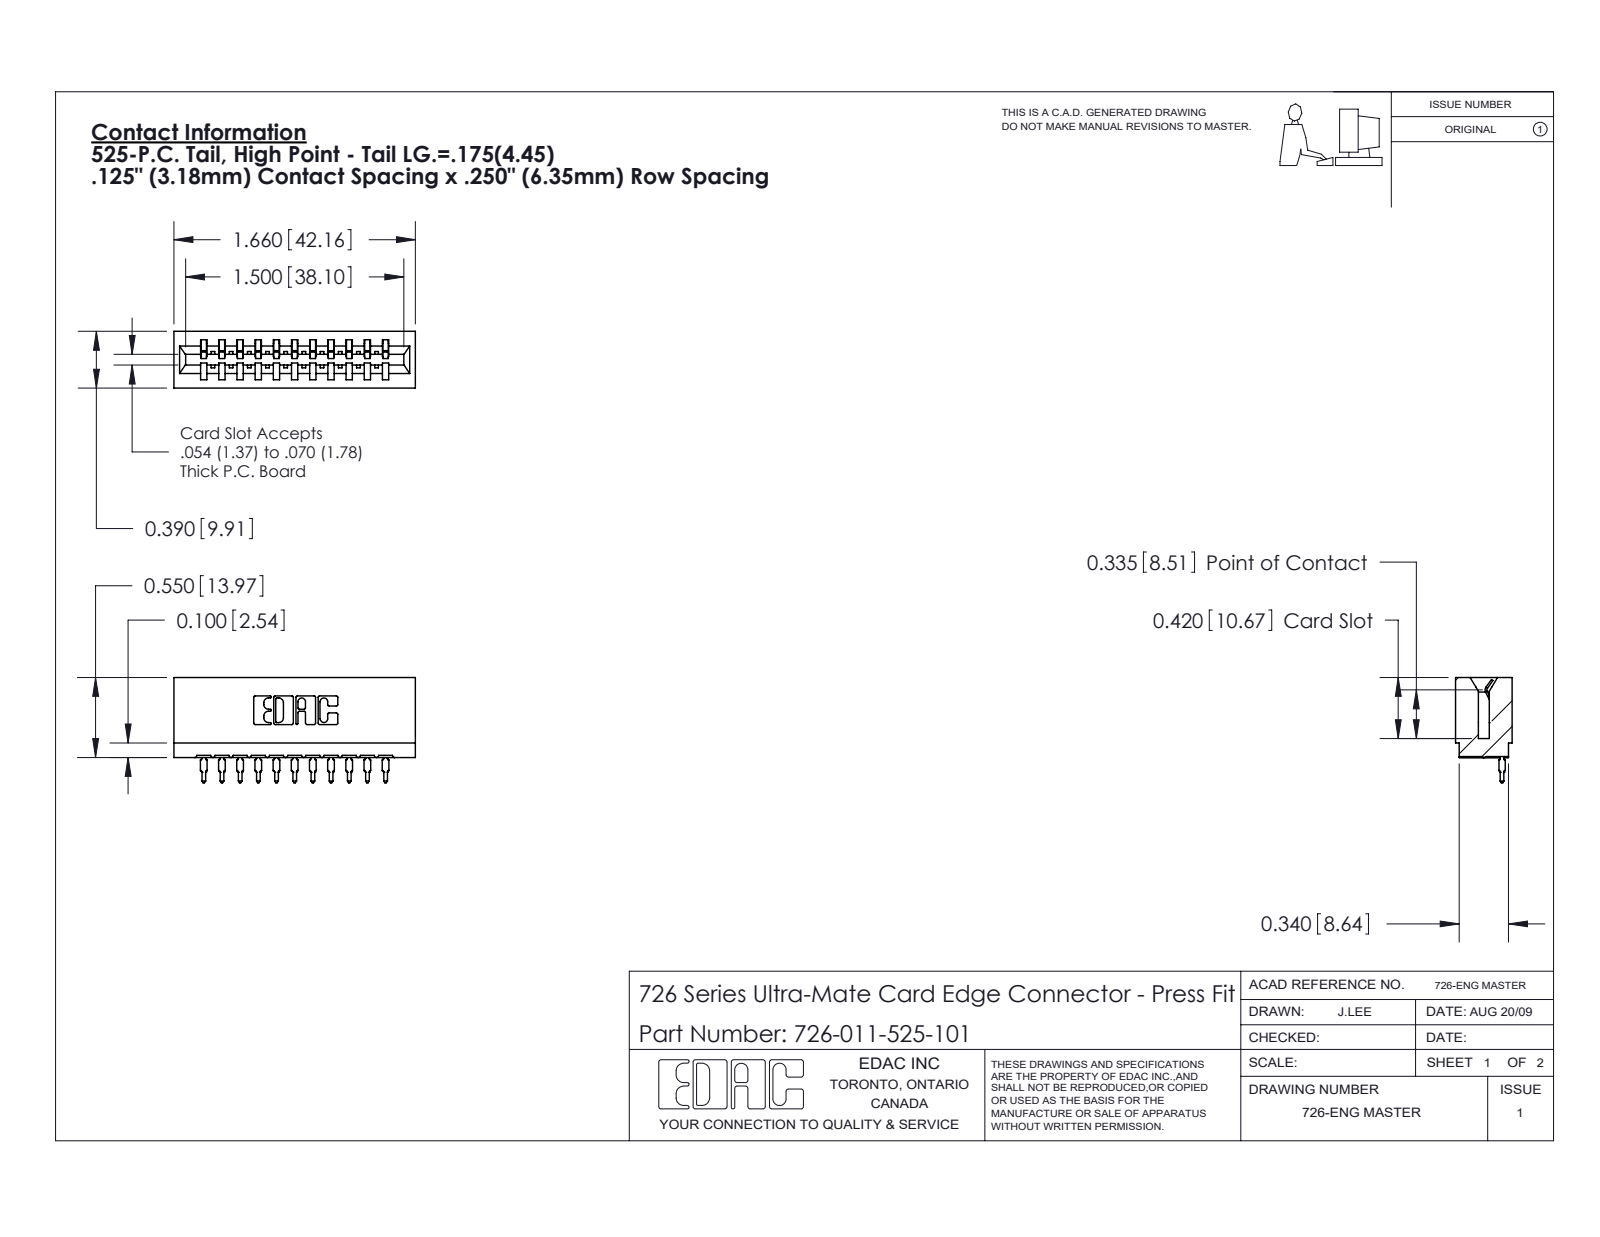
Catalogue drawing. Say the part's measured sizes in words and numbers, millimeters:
The part is named "726 Part_.515 Slot Depth - 01; 726-011-525-101; 746-292-001_525". Its 3-D file was written by "SolidWorks 2020 (CONFIG_CONTROL_DESIGN)". It is 12 solids with 1285 faces: 748 planar, 251 cylindrical and 286 other. Overall it measures 42.2 by 18.4 by 9.9 millimeters. Its volume is 3 930 cubic millimeters and its surface area 5 487 square millimeters. Partial cylindrical surfaces (rounded edges, fillets, slot ends): 22 of radius 0.3, 22 of radius 0.5, 12 of radius 0.4, 6 of radius 0.2, 6 of radius 0.8, 4 of radius 0.1, 4 of radius 0.3, 3 of radius 0.7. The main face-to-face distances are 6.4, 8.5, 1.4, 12.7, 19.1, 1.1, 3.2, 3.2, 9.9, 7.4.
